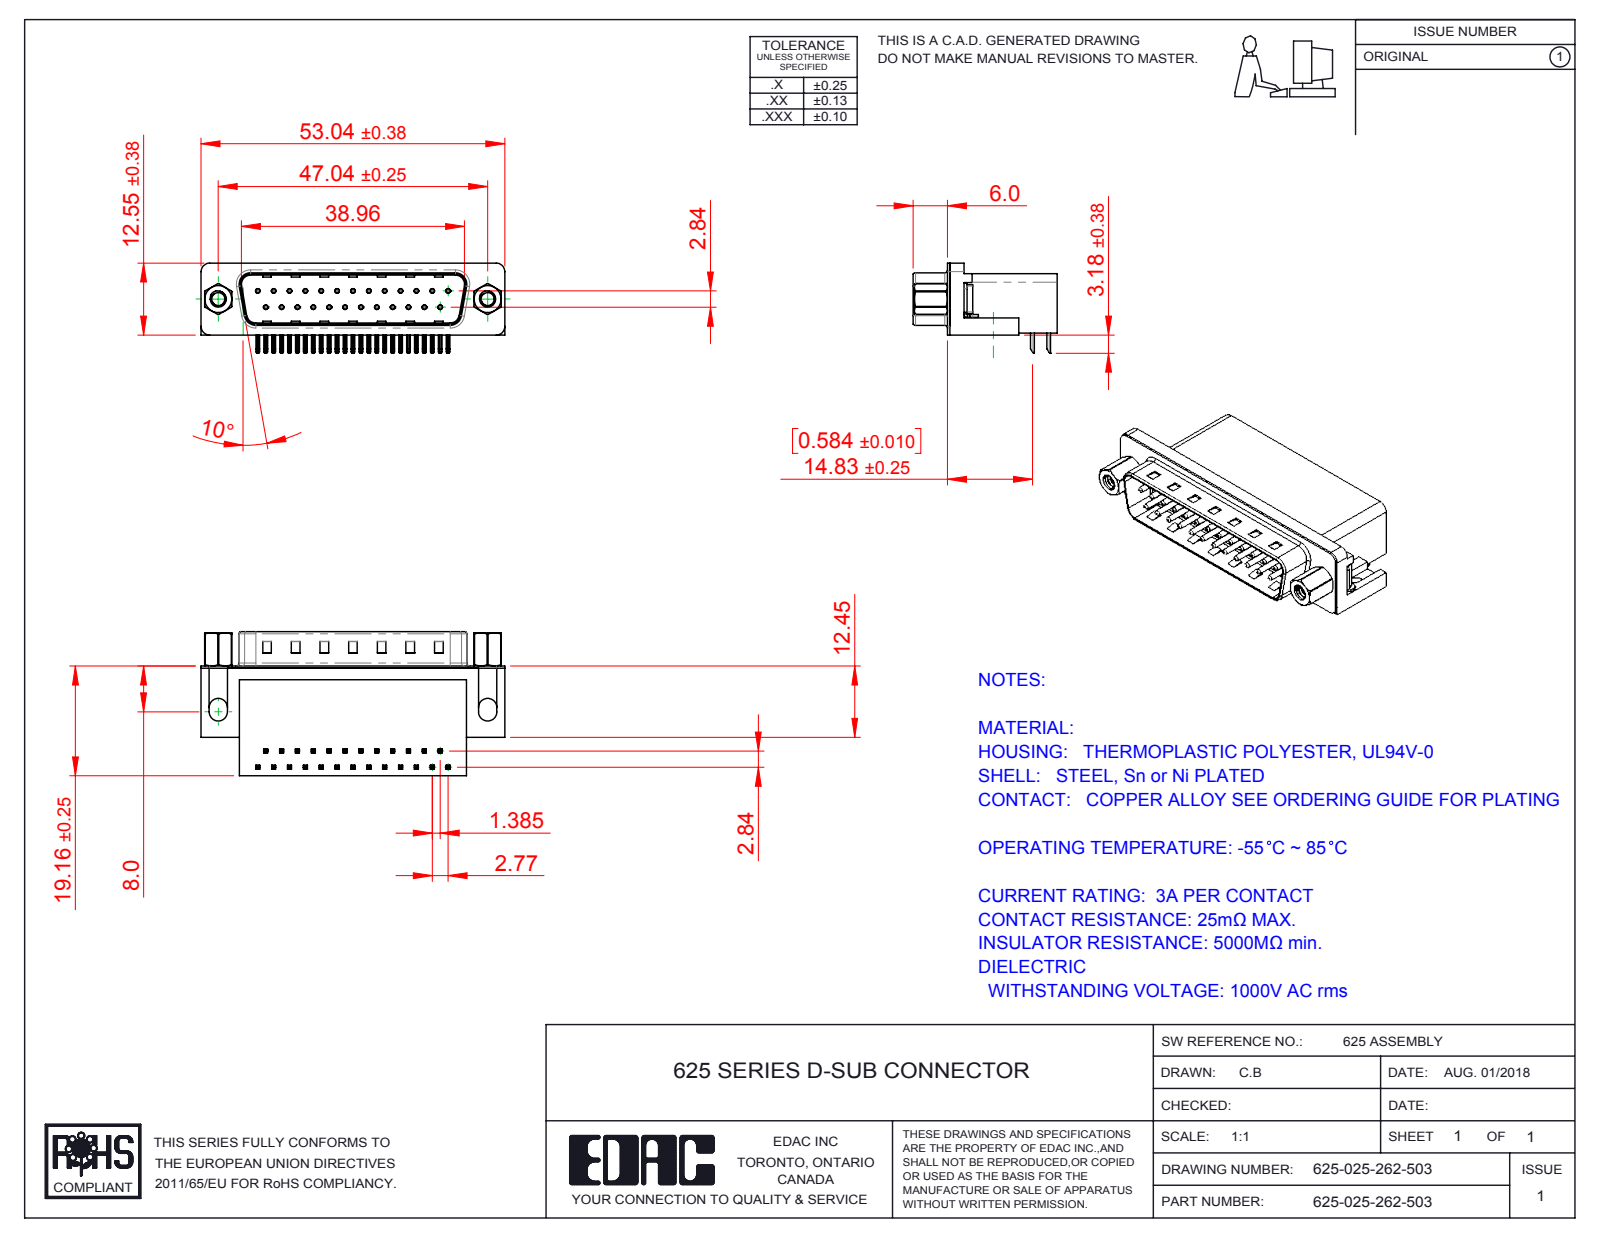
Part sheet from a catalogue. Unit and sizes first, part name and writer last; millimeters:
Units: millimetres
Overall size (bounding box): 53.04 × 25.16 × 15.73
Round holes (diameter × count): ⌀0.35 ×25, ⌀0.8 ×25, ⌀2.26 ×2, ⌀2.29 ×2, ⌀4 ×2, ⌀4.8 ×2, ⌀5 ×2
Round bosses / shafts (diameter × count): ⌀0.75 ×25, ⌀4.9 ×2, ⌀4.75 ×2, ⌀3.9 ×2, ⌀2.79 ×2
Partial cylindrical surfaces — rounded edges, fillets, slot ends (radius × count): R0.25 ×108, R0.12 ×50, R1 ×16, R0.5 ×9, R1.6 ×8, R1.5 ×7, R0.9 ×4, R2 ×4
Main face-to-face distances: 0.4, 10.35, 18.76, 2.1, 8.76, 10.46, 10.86, 1.7, 19.16, 10.11
Hole centre spacings: 3.16, 2.77, 11.08, 5.54, 8.31, 5.03, 13.85, 7.48
Volume: 9 350 mm³ · Surface area: 9 211 mm²
Bodies: 33 solids, 2389 faces (1429 planar, 729 cylindrical, 231 other)
Part name (STEP PRODUCT): 625 4-40 Threaded Rivet; 625-025-262-503; 625 4-40 Hex Standoff 5; 625 Housing_25 Socket (+4 more)
STEP written by: SolidWorks 2016 (CONFIG_CONTROL_DESIGN)
